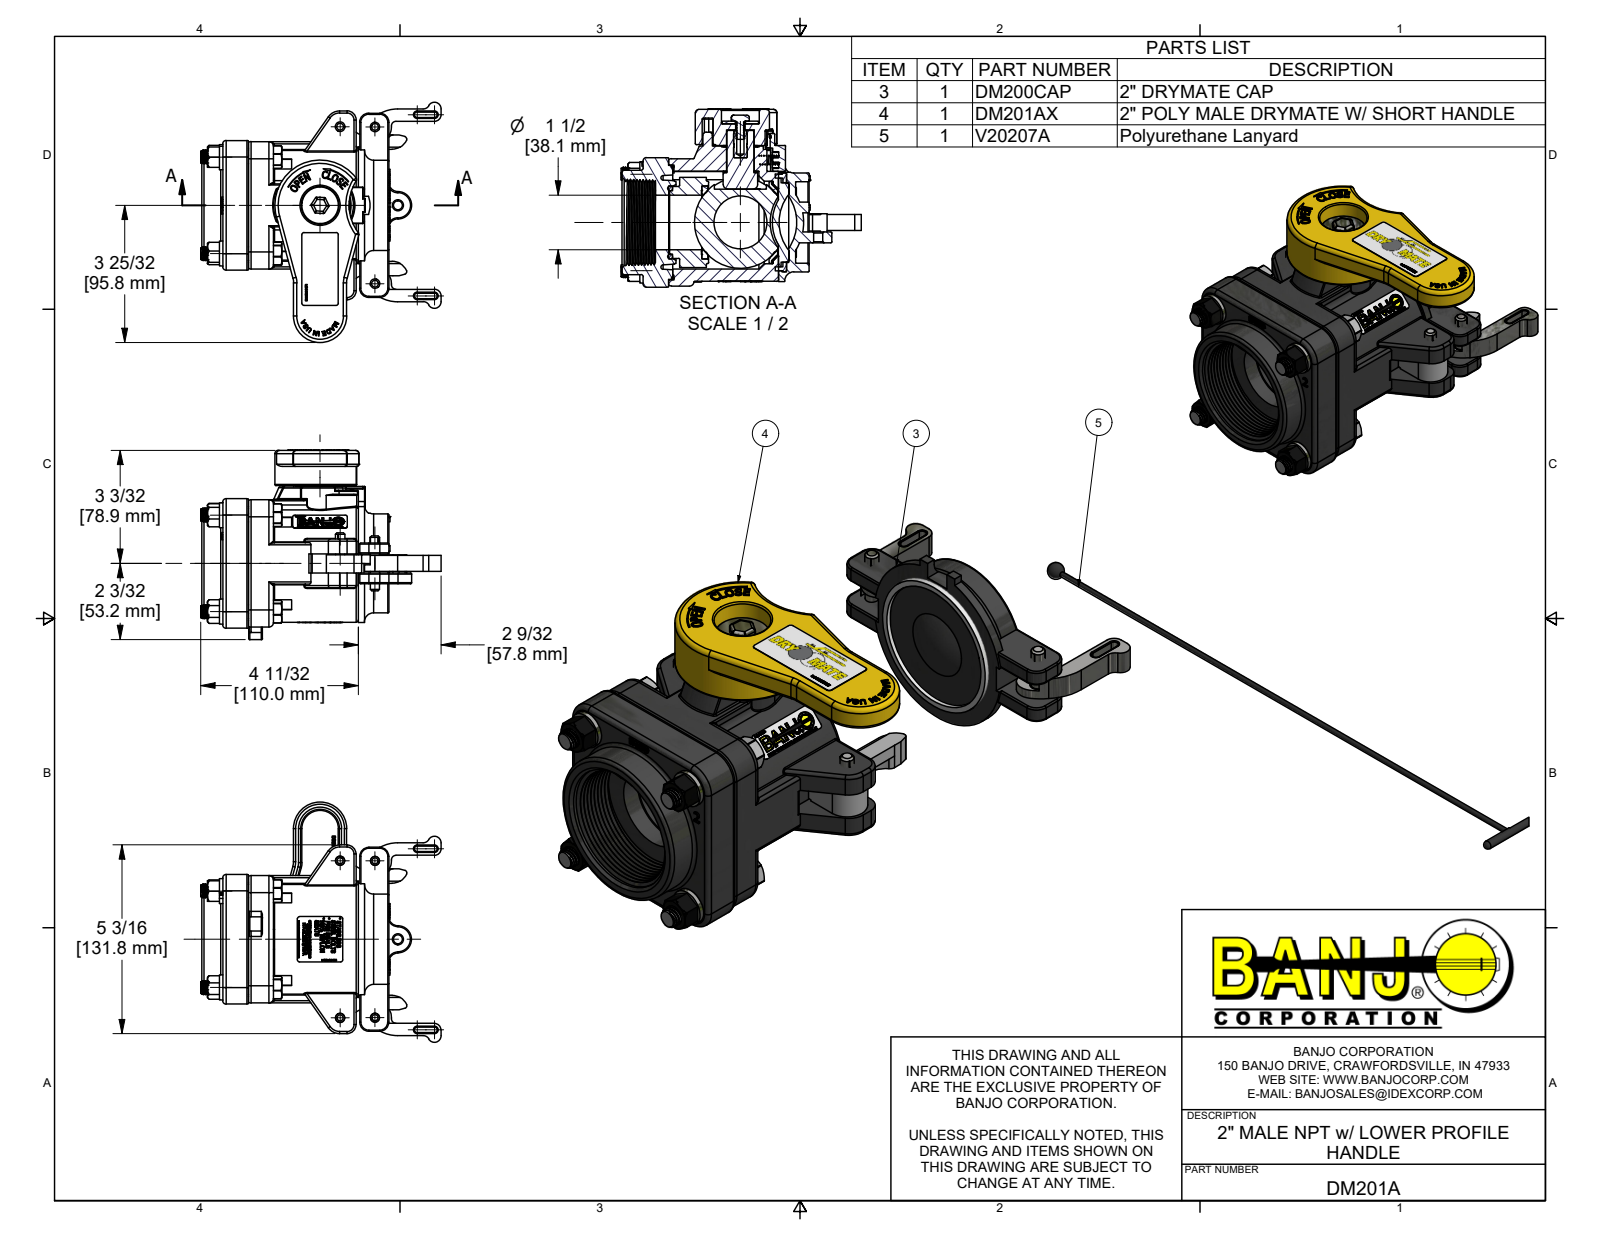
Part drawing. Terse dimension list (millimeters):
name: DM201A; DM201AX; DM20254; DM20254MY (+8 more)
written by: Autodesk Inventor 2022 (AUTOMOTIVE_DESIGN)
unit: mm
bodies: 44 solids, 6036 faces (2854 planar, 891 cylindrical, 2291 other)
size: 167.8 × 167.6 × 132.5
volume: 708 700 mm³; area: 249 800 mm²
holes: 5× ⌀6.4, 5× ⌀9.5, 4× ⌀6.5, 4× ⌀7.8, 4× ⌀9.8, 4× ⌀10.3, 4× ⌀10.7, 3× ⌀3.2, 1× ⌀5, 1× ⌀5.1, 1× ⌀5.8, 1× ⌀6.6
bosses: 60× ⌀8.2, 4× ⌀17.4, 4× ⌀9.5, 4× ⌀6.6, 4× ⌀6.3, 3× ⌀7.1, 2× ⌀63, 1× ⌀82.6
rounds: 107× R0.8, 47× R1.5, 20× R0.5, 18× R2.3, 12× R0.3, 10× R3.2, 8× R4.1, 8× R6.4
face distances: 5.6, 7.6, 94.6, 7.5, 0.8, 89.7, 20.9, 20.9, 17.8, 76.8
hole spacings: 67.4, 47.5, 47.8, 66.8, 67.3, 67.5, 95.3, 24.1
